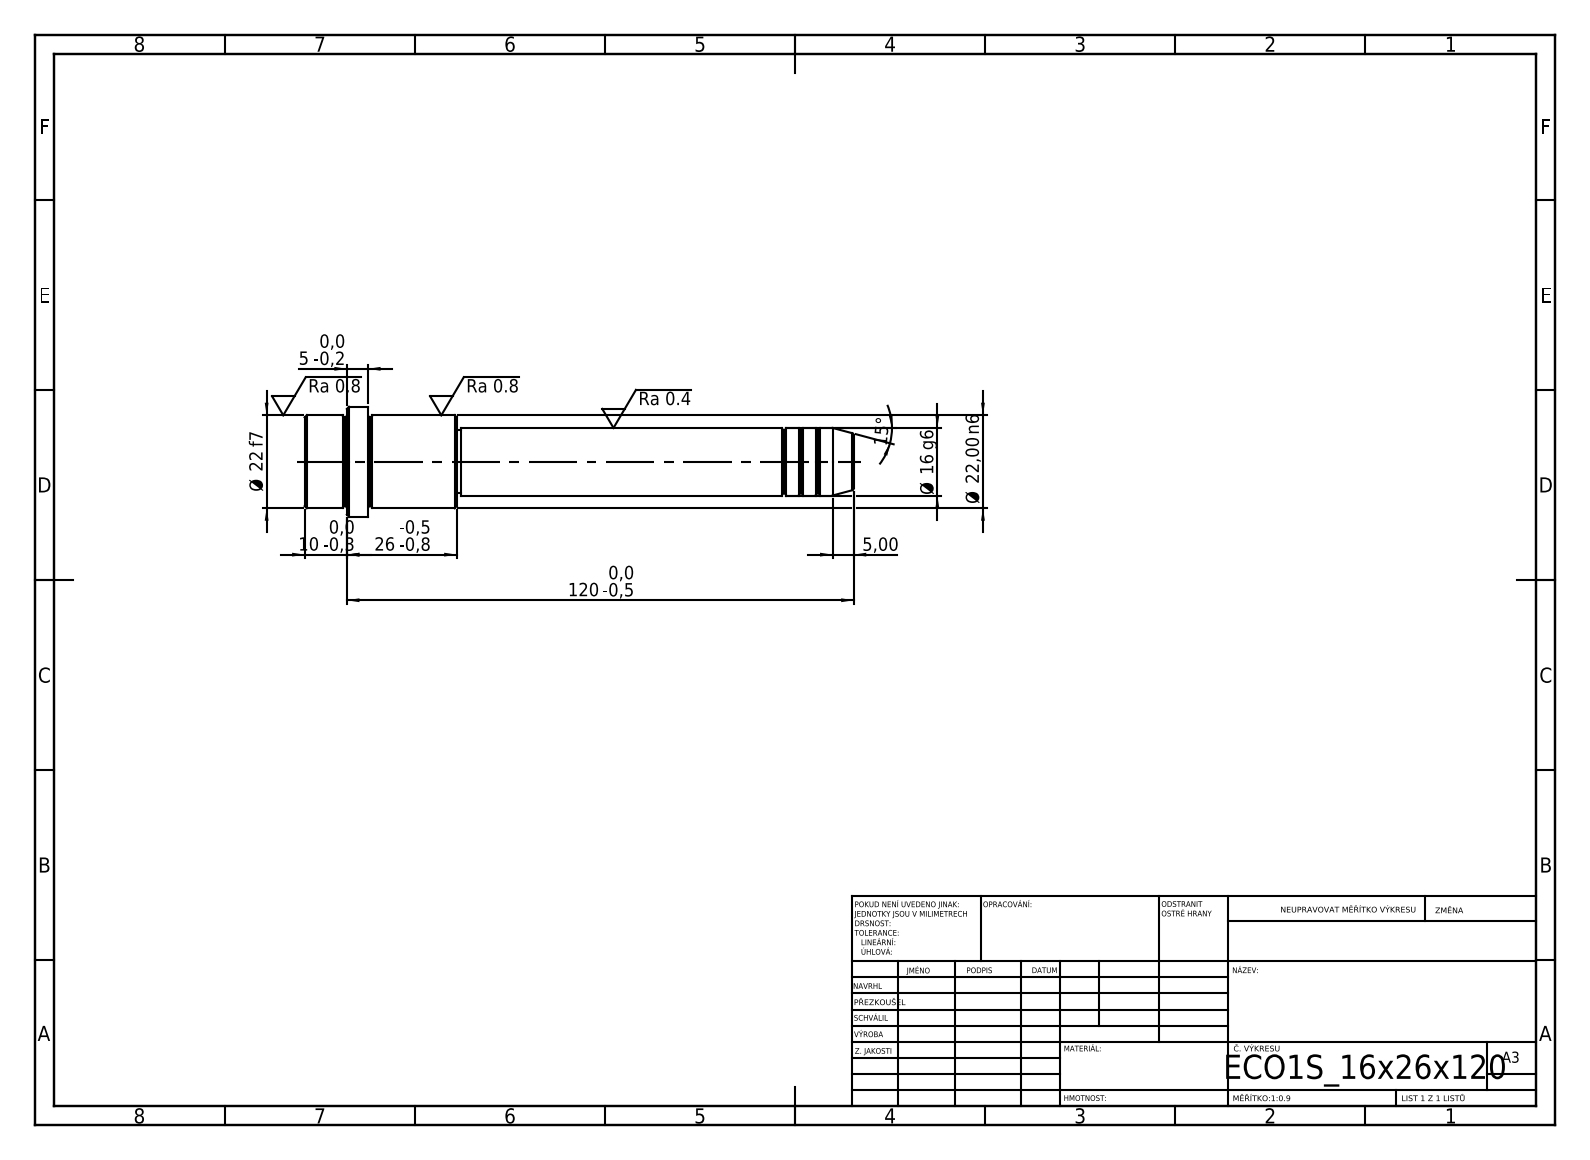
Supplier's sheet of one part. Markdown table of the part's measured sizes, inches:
| quantity | value |
| --- | --- |
| STEP written by | SolidWorks 2019 (CONFIG_CONTROL_DESIGN) |
| units | inches |
| bodies | 1 solid, 52 faces (6 planar, 16 cylindrical, 30 other) |
| overall size | 5.118 × 1.024 × 1.024 |
| volume | 2.015 in³ |
| surface area | 13 in² |
| round bosses / shafts (diameter × count) | 1.024 × 1, 0.866 × 1, 0.63 × 1, 0.591 × 1 |
| main face-to-face distances | 1.417, 0.827, 0.591, 3.701, 4.528, 5.118, 4.724, 1.024, 0.197, 0.394 |
